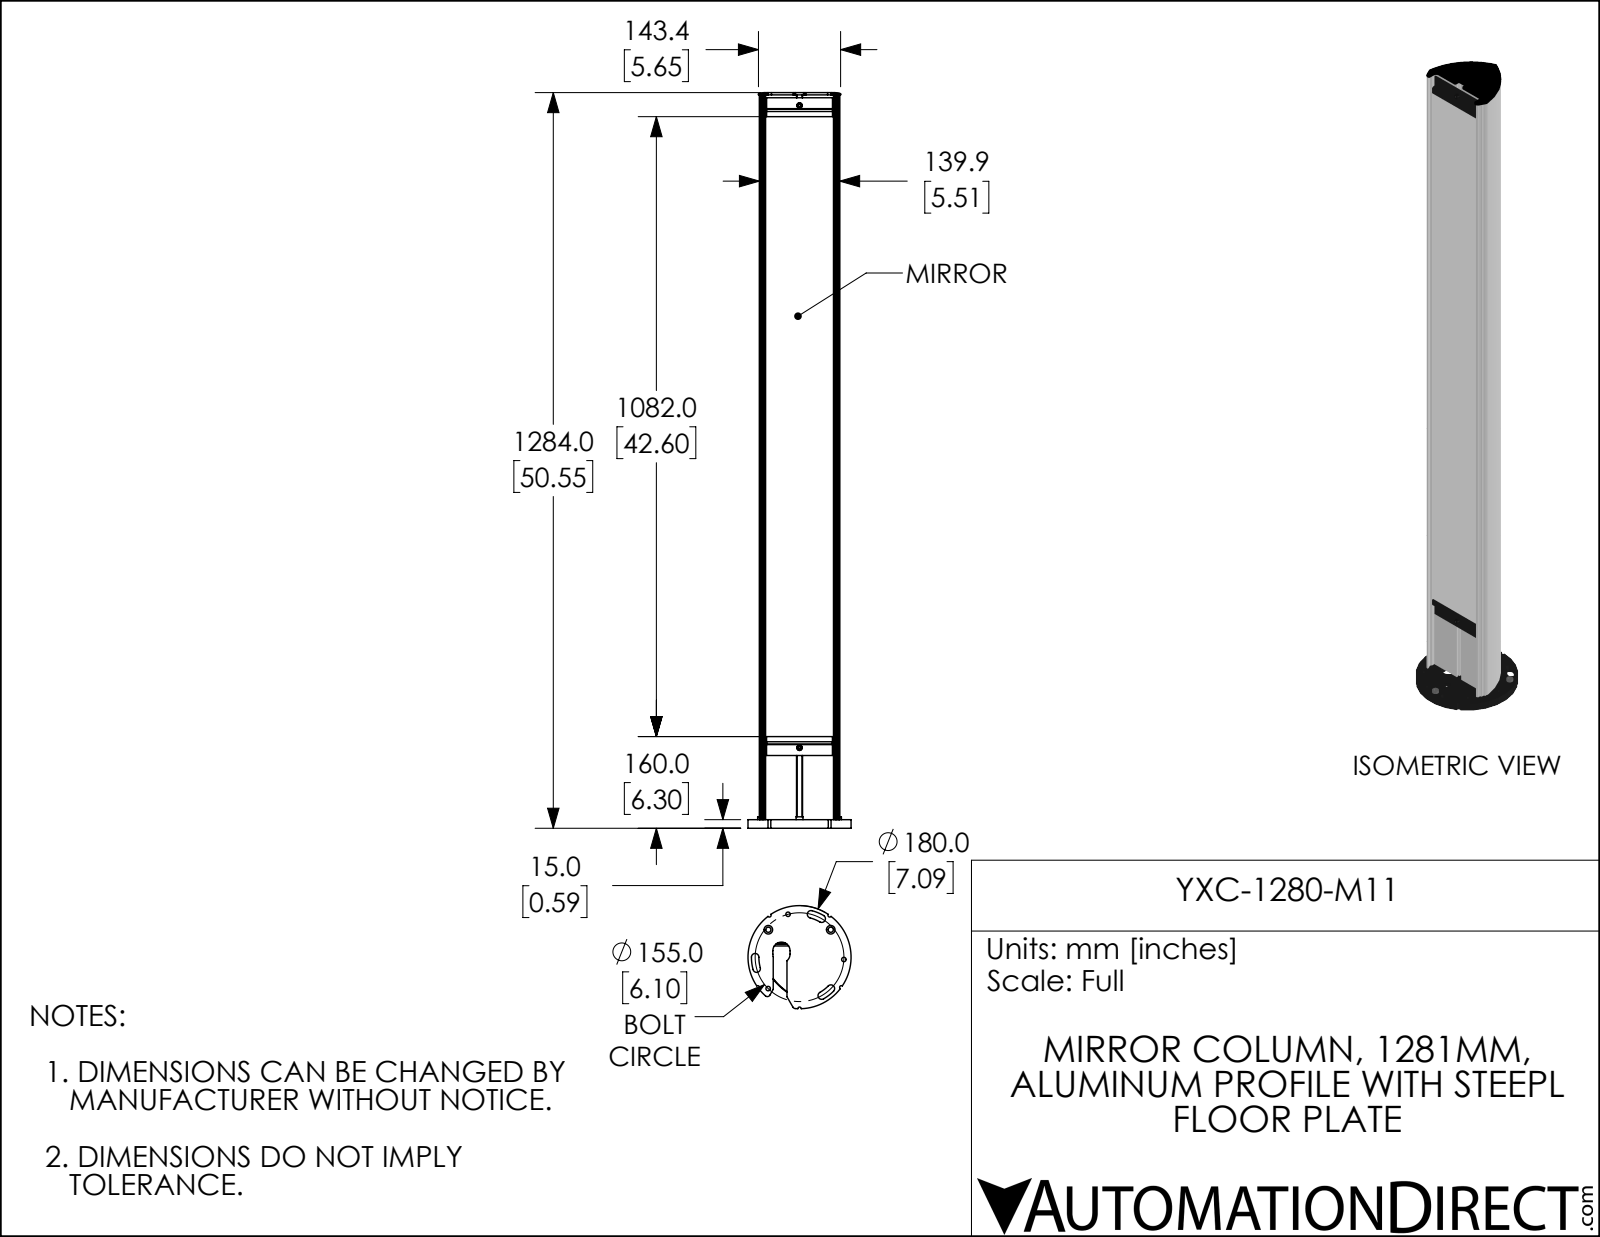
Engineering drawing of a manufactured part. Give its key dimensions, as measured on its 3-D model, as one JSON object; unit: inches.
{"part_name": "YXC-1280-M11", "step_written_by": "SolidWorks 2019 (AUTOMOTIVE_DESIGN)", "units": "inches", "bodies": {"solids": 1, "faces": 290, "planar": 187, "cylindrical": 88, "other": 15}, "overall_size": [50.551, 7.087, 7.085], "volume_in3": 745.7, "surface_area_in2": 1073, "round_holes": [[0.307, 3], [0.591, 3], [0.354, 2], [0.173, 1]], "round_bosses_or_shafts": [[0.472, 3], [0.374, 2], [0.335, 2], [7.087, 1]], "partial_cylinders_radius": [[0.118, 9], [0.256, 6], [0.236, 5], [0.039, 4], [0.052, 4], [4.685, 4], [0.197, 3], [0.052, 2]], "face_to_face_distances": [0.157, 0.118, 0.591, 0.335, 0.492, 0.453, 0.098, 50.551, 49.961, 0.382], "hole_center_spacings": [2.146, 1.255, 1.257, 1.722, 2.235, 3.121, 3.717, 3.719]}
